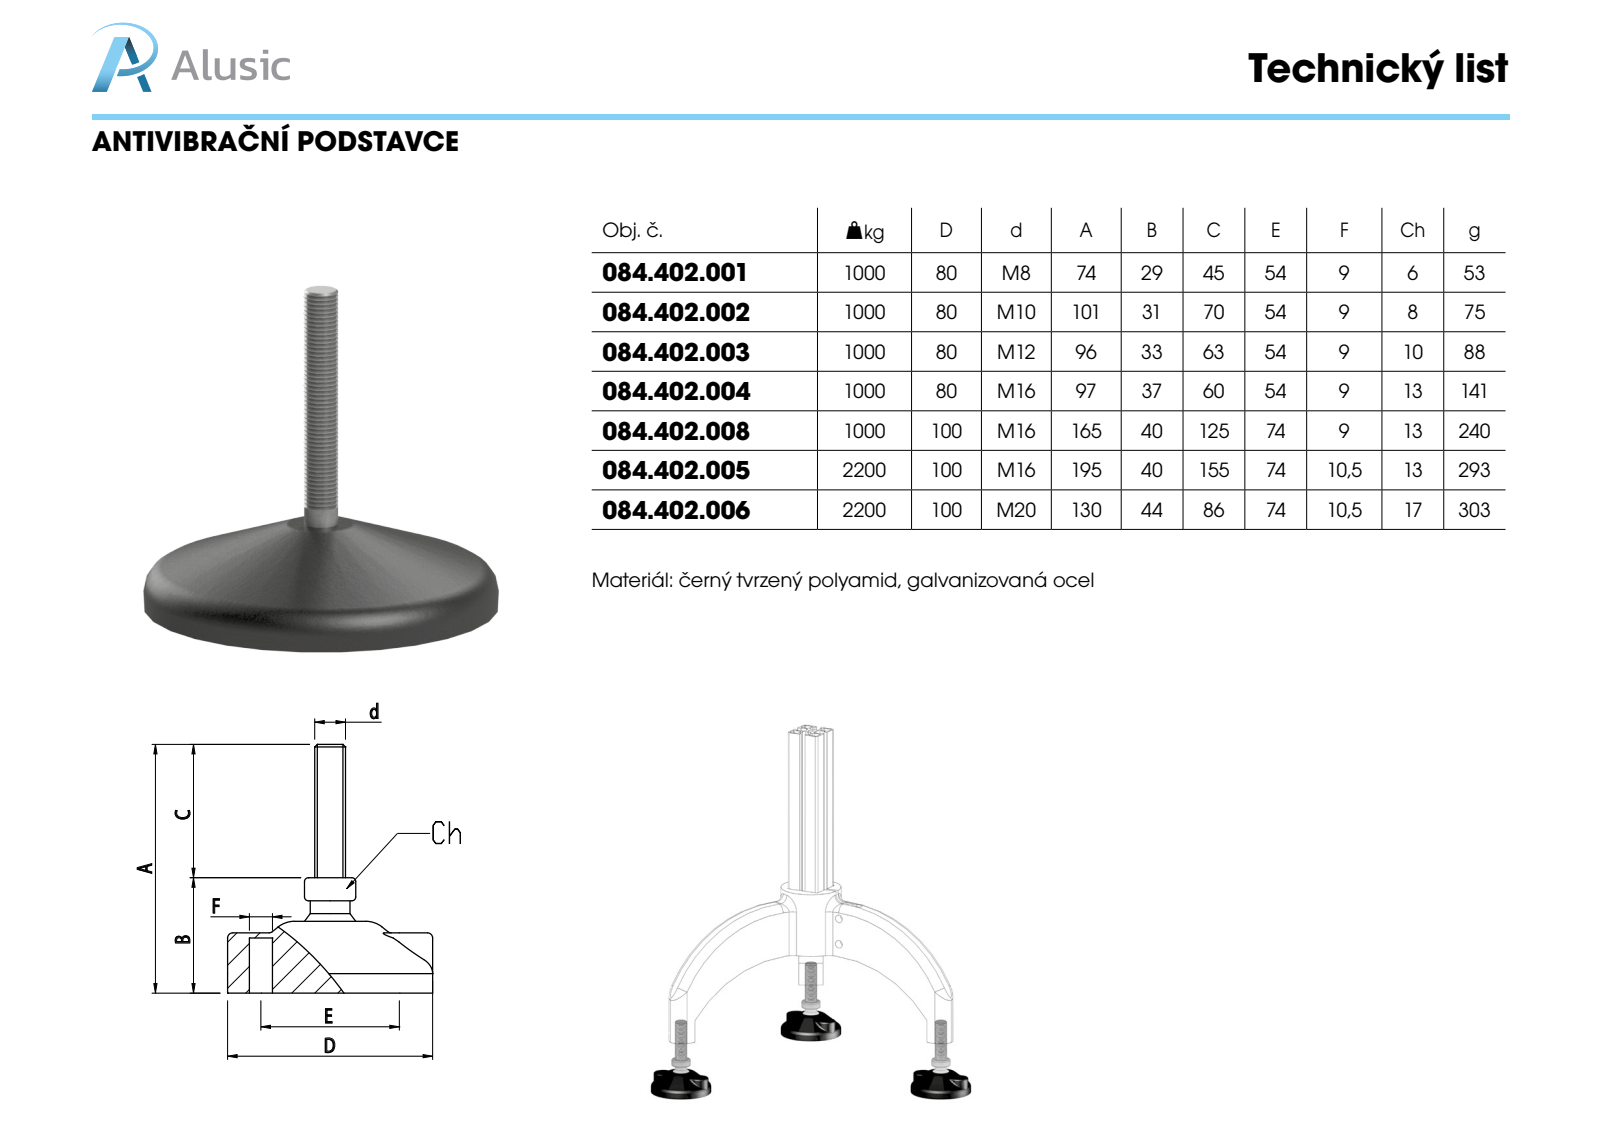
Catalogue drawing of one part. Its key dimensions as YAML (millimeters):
part_name: "084.402.005"
step_written_by: "SolidWorks 2011 (CONFIG_CONTROL_DESIGN)"
units: millimeters
bodies: {solids: 2, faces: 61, planar: 12, cylindrical: 14, other: 35}
overall_size: [195, 100, 100]
volume: 191086
surface_area: 30249
round_bosses_or_shafts:
  - {diameter: 100, count: 1}
  - {diameter: 25, count: 1}
  - {diameter: 16, count: 1}
  - {diameter: 15.5, count: 1}
partial_cylinders:
  - {radius: 2, count: 2}
  - {radius: 13, count: 2}
face_to_face_distances: [28, 23.5, 4.5, 39, 15.5, 11, 48, 24.5, 20, 9]
